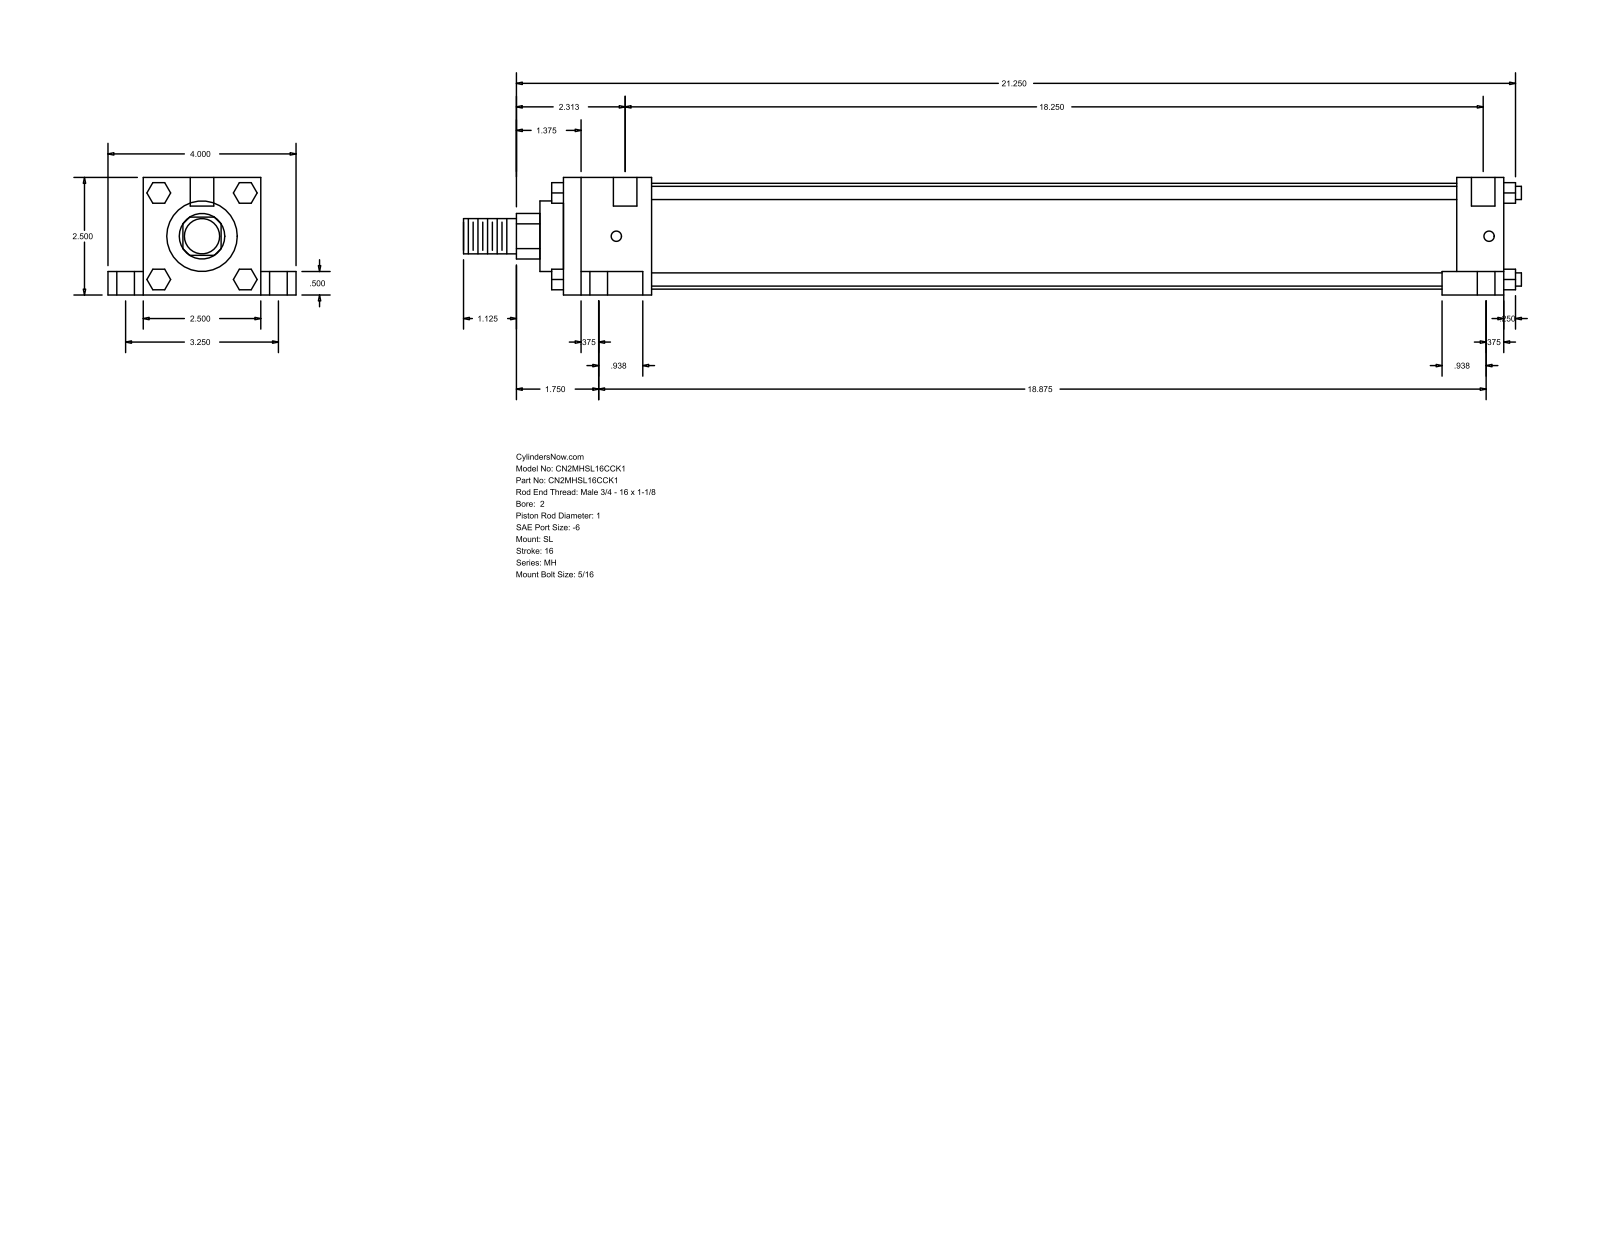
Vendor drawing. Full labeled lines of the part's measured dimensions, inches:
Part name (STEP PRODUCT): MH_SL__0200_1
STEP written by: GSSL Pune (CONFIG_CONTROL_DESIGN)
Units: inches
Bodies: 0 solids, 148 faces (112 planar, 36 cylindrical, 0 other)
Overall size (bounding box): 22.5 × 4 × 2.5
Round holes (diameter × count): ⌀0.219 ×4, ⌀0.375 ×4, ⌀0.625 ×4, ⌀0.5 ×2
Round bosses / shafts (diameter × count): ⌀0.281 ×4, ⌀2.25 ×1, ⌀1.5 ×1, ⌀1 ×1, ⌀0.75 ×1
Partial cylindrical surfaces — rounded edges, fillets, slot ends (radius × count): R0.484 ×1
Main face-to-face distances: 2.5, 20, 0.5, 0.75, 2, 3.25, 1, 19, 1.875, 17.125
Hole centre spacings: 1.626, 1.668, 1.719, 3.25, 18.385, 18.562, 18.571, 18.875
